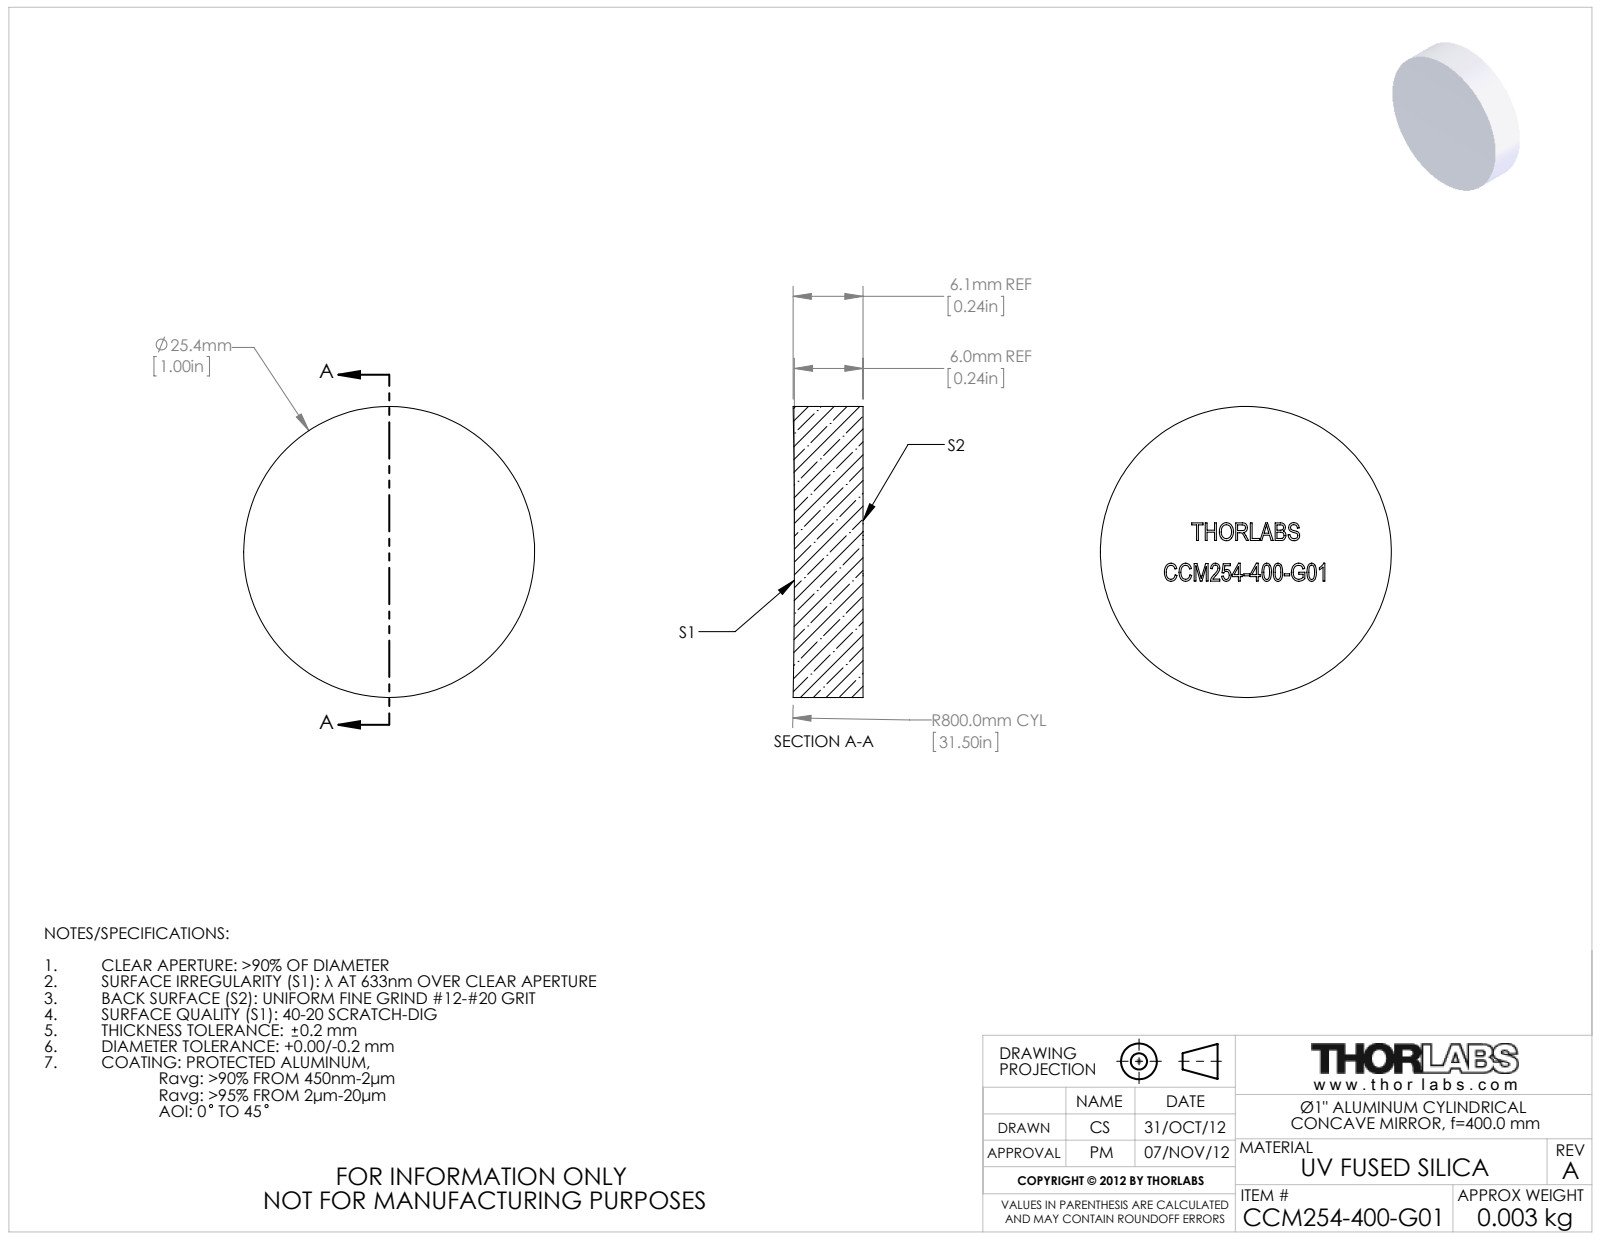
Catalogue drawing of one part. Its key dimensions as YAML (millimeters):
part_name: "TTN005973-E0W"
step_written_by: "SolidWorks 2012 (CONFIG_CONTROL_DESIGN)"
units: millimeters
bodies: {solids: 1, faces: 37, planar: 33, cylindrical: 4, other: 0}
overall_size: [25.4, 25.4, 6.1]
volume: 3053
surface_area: 1496
round_bosses_or_shafts:
  - {diameter: 25.4, count: 1}
partial_cylinders:
  - {radius: 800, count: 1}
